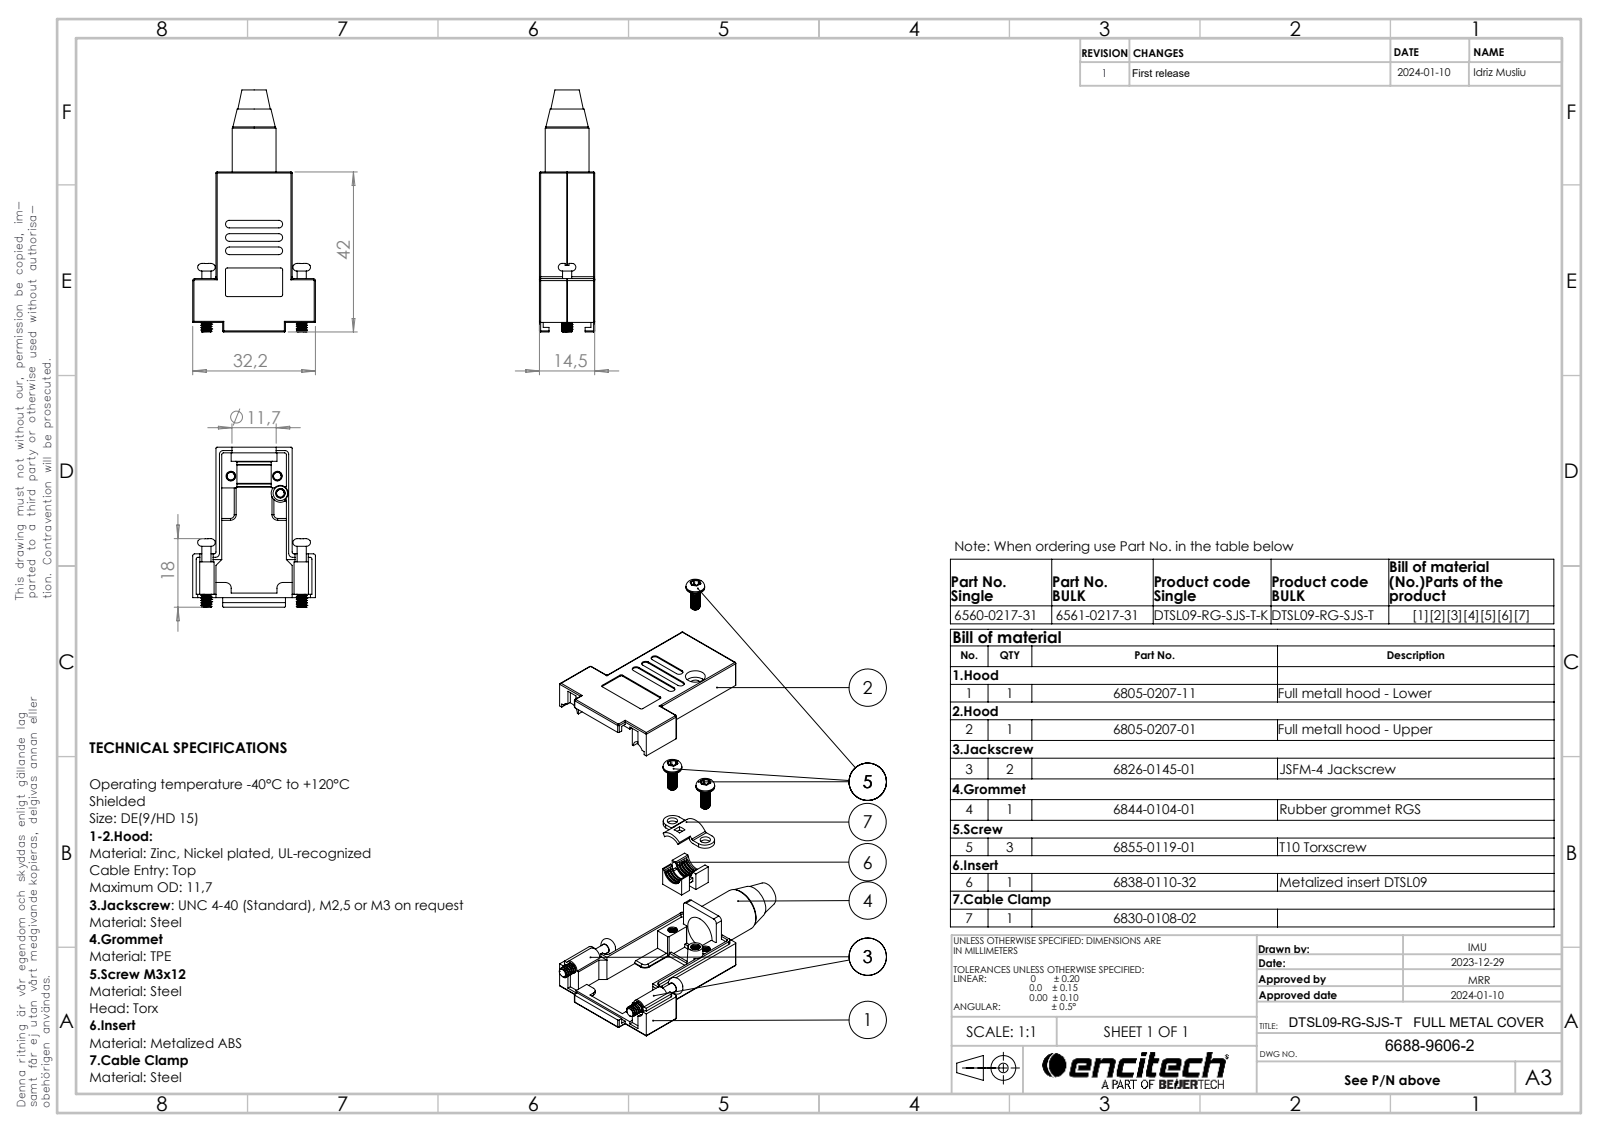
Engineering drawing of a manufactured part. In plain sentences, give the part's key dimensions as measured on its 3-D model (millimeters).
The part is named "6830-0108-02; 6805-0207-01; 6844-0104-01; 6838-0110-32 (+4 more)". Its 3-D file was written by "SolidWorks 2021 (AUTOMOTIVE_DESIGN)". It is 10 solids with 943 faces: 385 planar, 460 cylindrical and 98 other. Overall it measures 63.5 by 32.2 by 14.5 millimeters. Its volume is 6 598 cubic millimeters and its surface area 10 983 square millimeters. Round holes: 2 of diameter 2.3, 2 of diameter 2.7, 2 of diameter 3, 2 of diameter 3.5, 1 of diameter 2, 1 of diameter 2.6, 1 of diameter 5.2, 1 of diameter 9, 1 of diameter 11.6. Round bosses or shafts: 3 of diameter 4.9, 3 of diameter 2.5, 2 of diameter 2.8, 2 of diameter 2.4, 1 of diameter 11.5, 1 of diameter 11.1. Partial cylindrical surfaces (rounded edges, fillets, slot ends): 28 of radius 0.3, 23 of radius 0.5, 21 of radius 1, 18 of radius 0.18, 18 of radius 0.7, 16 of radius 0.25, 9 of radius 1.5, 3 of radius 2. The main face-to-face distances are 1, 13.5, 14.5, 12.5, 1.5, 6.25, 7.25, 0.7, 20, 18.5. The hole center spacings are 12.5, 4.57, 12.2, 13.76, 25.
